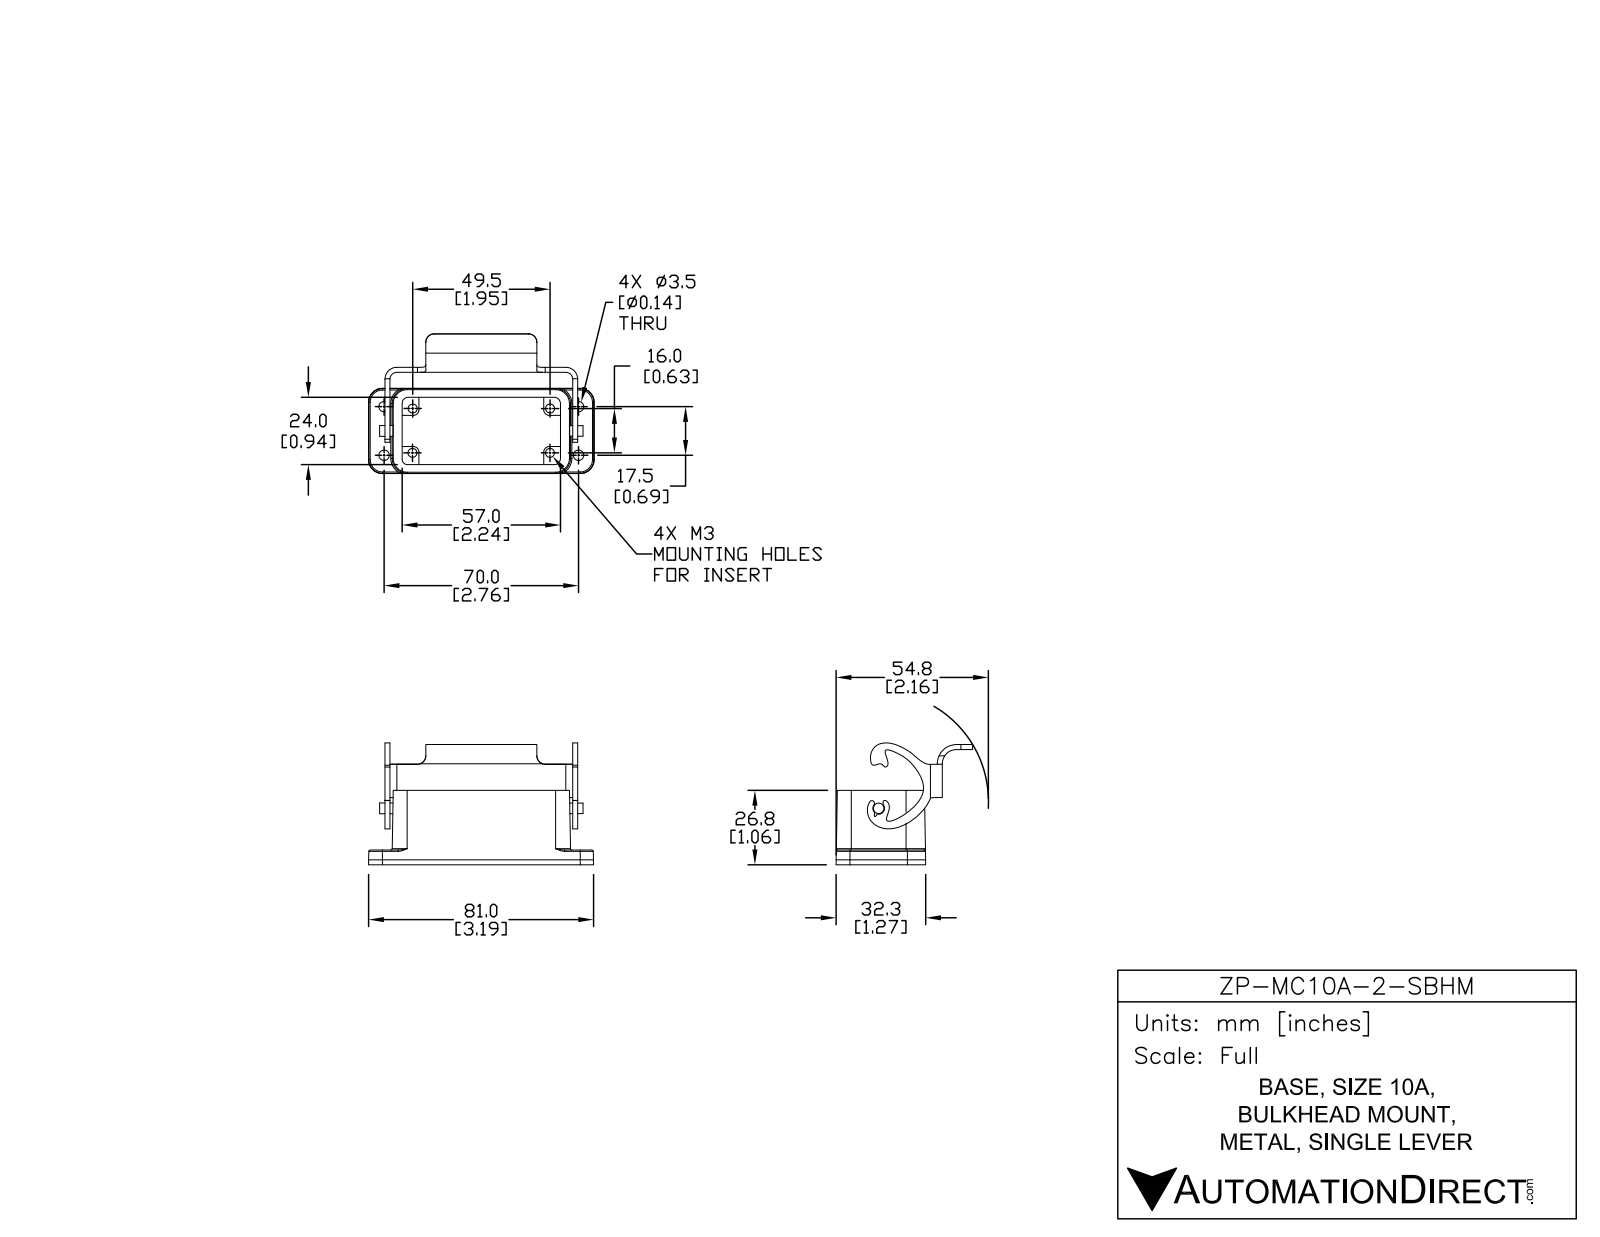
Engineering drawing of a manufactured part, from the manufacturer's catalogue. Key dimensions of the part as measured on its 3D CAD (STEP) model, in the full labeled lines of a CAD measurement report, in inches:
Part name (STEP PRODUCT): ZP-MC10A-2-SBHM
STEP written by: SolidWorks 2014 (AUTOMOTIVE_DESIGN)
Units: inches
Bodies: 2 solids, 159 faces (58 planar, 57 cylindrical, 44 other)
Overall size (bounding box): 3.197 × 1.979 × 1.734
Volume: 1.205 in³ · Surface area: 26.21 in²
Round holes (diameter × count): ⌀0.118 ×4, ⌀0.138 ×4
Round bosses / shafts (diameter × count): ⌀0.154 ×1, ⌀0.15 ×1
Partial cylindrical surfaces — rounded edges, fillets, slot ends (radius × count): R0.02 ×6, R0.079 ×4, R0.118 ×4, R0.098 ×2, R0.169 ×2, R0.083 ×1, R0.201 ×1, R0.272 ×1
Main face-to-face distances: 0.109, 0.071, 0.109, 1.063, 2.661, 0.217, 0.846, 1.711, 1.494, 0.648
Hole centre spacings: 0.405, 0.773, 2.352, 2.443, 0.63, 0.689, 1.949, 2.048
